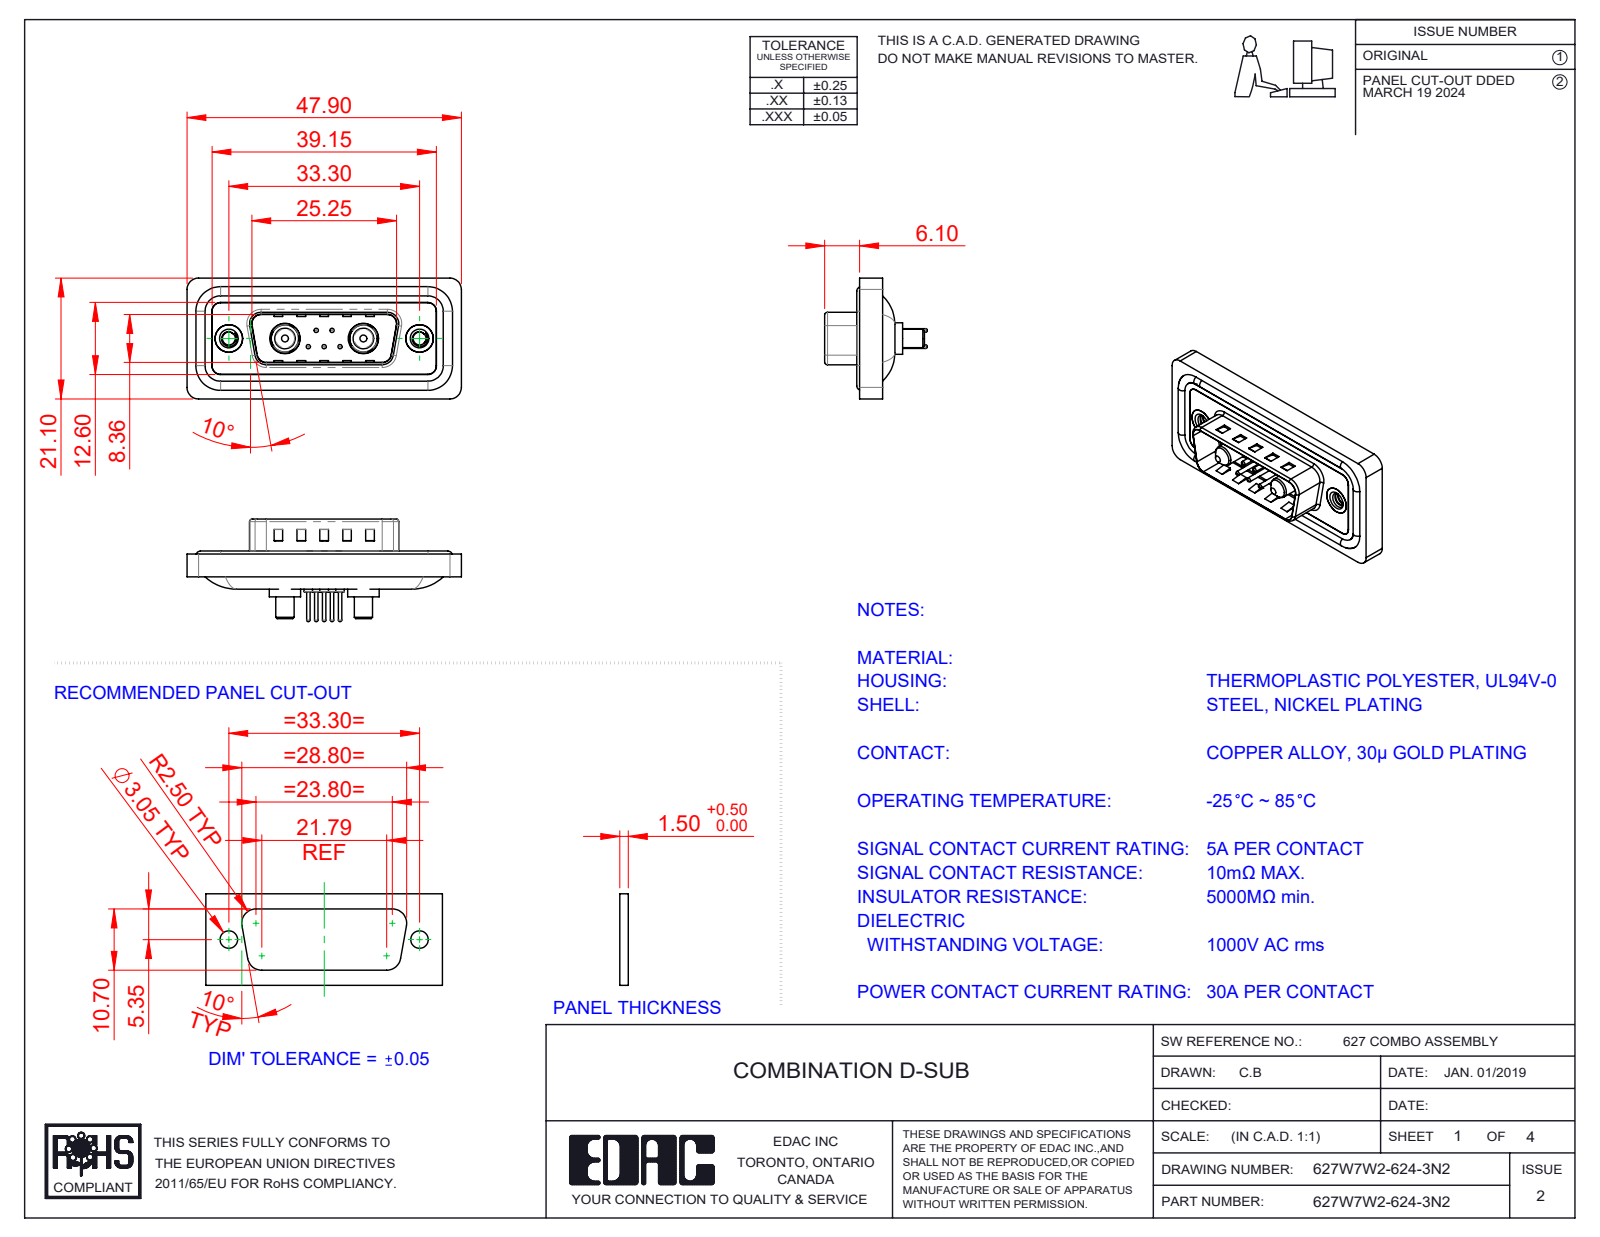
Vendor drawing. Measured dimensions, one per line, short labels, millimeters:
name: 627W7W2-624-3N2; 627Combo Shell Front_15 Contacts; Power Pin_30A S; 627Combo Waterproof Housing_15 Contacts (+5 more)
written by: SolidWorks 2023 (CONFIG_CONTROL_DESIGN)
unit: mm
bodies: 16 solids, 710 faces (232 planar, 292 cylindrical, 186 other)
size: 47.9 × 21.1 × 17.9
volume: 5 531 mm³; area: 8 802 mm²
holes: 5× ⌀0.75, 5× ⌀1.6, 5× ⌀2, 2× ⌀2.26, 2× ⌀4, 2× ⌀4.8, 2× ⌀4.85, 2× ⌀5, 2× ⌀5.3
bosses: 5× ⌀1.5, 5× ⌀0.6, 4× ⌀1.6, 2× ⌀5.5, 2× ⌀5.2, 2× ⌀4.9, 2× ⌀4.75, 2× ⌀3.75
rounds: 26× R1.5, 20× R2, 8× R0.5, 8× R1.6, 4× R0.25, 4× R0.6, 4× R0.65, 4× R0.9
face distances: 0.4, 1.1, 1.5, 1.6, 0.5, 3.1, 2.9, 0.82, 9.58, 2.5
hole spacings: 3.16, 2.77, 9.8, 23.5, 4.31, 4.33, 5.03, 5.04
